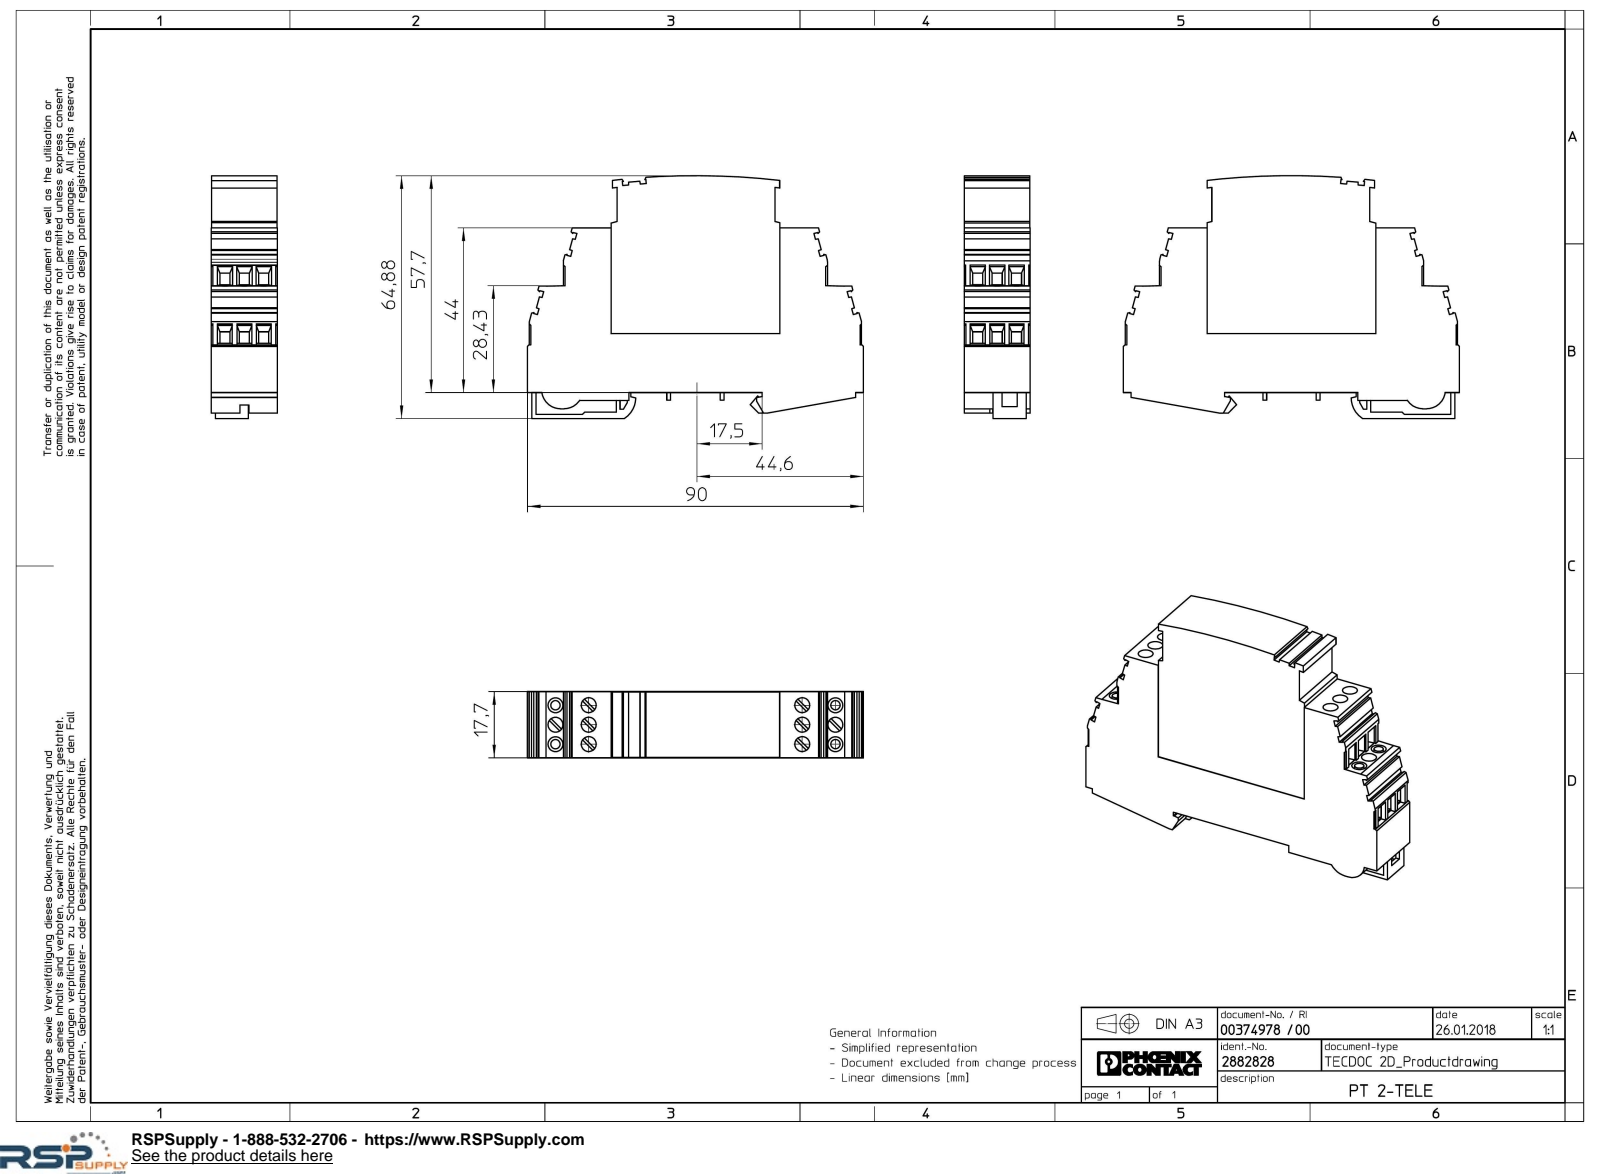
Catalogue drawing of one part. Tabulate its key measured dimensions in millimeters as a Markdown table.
| quantity | value |
| --- | --- |
| part name | PT_2_TELE-select |
| STEP written by | Creo Elements/Direct Modeling 18.1I 14-Aug-2016 (C) Parametric Technology GmbH (AUTOMOTIVE_DESIGN) |
| units | millimeters |
| bodies | 1 solid, 454 faces (414 planar, 24 cylindrical, 16 other) |
| overall size | 90 × 64.88 × 17.7 |
| volume | 74 053 mm³ |
| surface area | 17 952 mm² |
| round holes (diameter × count) | 4 × 6 |
| round bosses / shafts (diameter × count) | 2.5 × 2 |
| partial cylindrical surfaces (radius × count) | 5 × 2, 3 × 1, 6.5 × 1, 198 × 1, 200 × 1 |
| main face-to-face distances | 17.6, 17.7, 17.5, 5.2, 4.48, 2.7, 44, 7.5, 0.75, 15.3 |
| hole center spacings | 5.2, 57.44, 57.2, 10.4, 58.14 |
